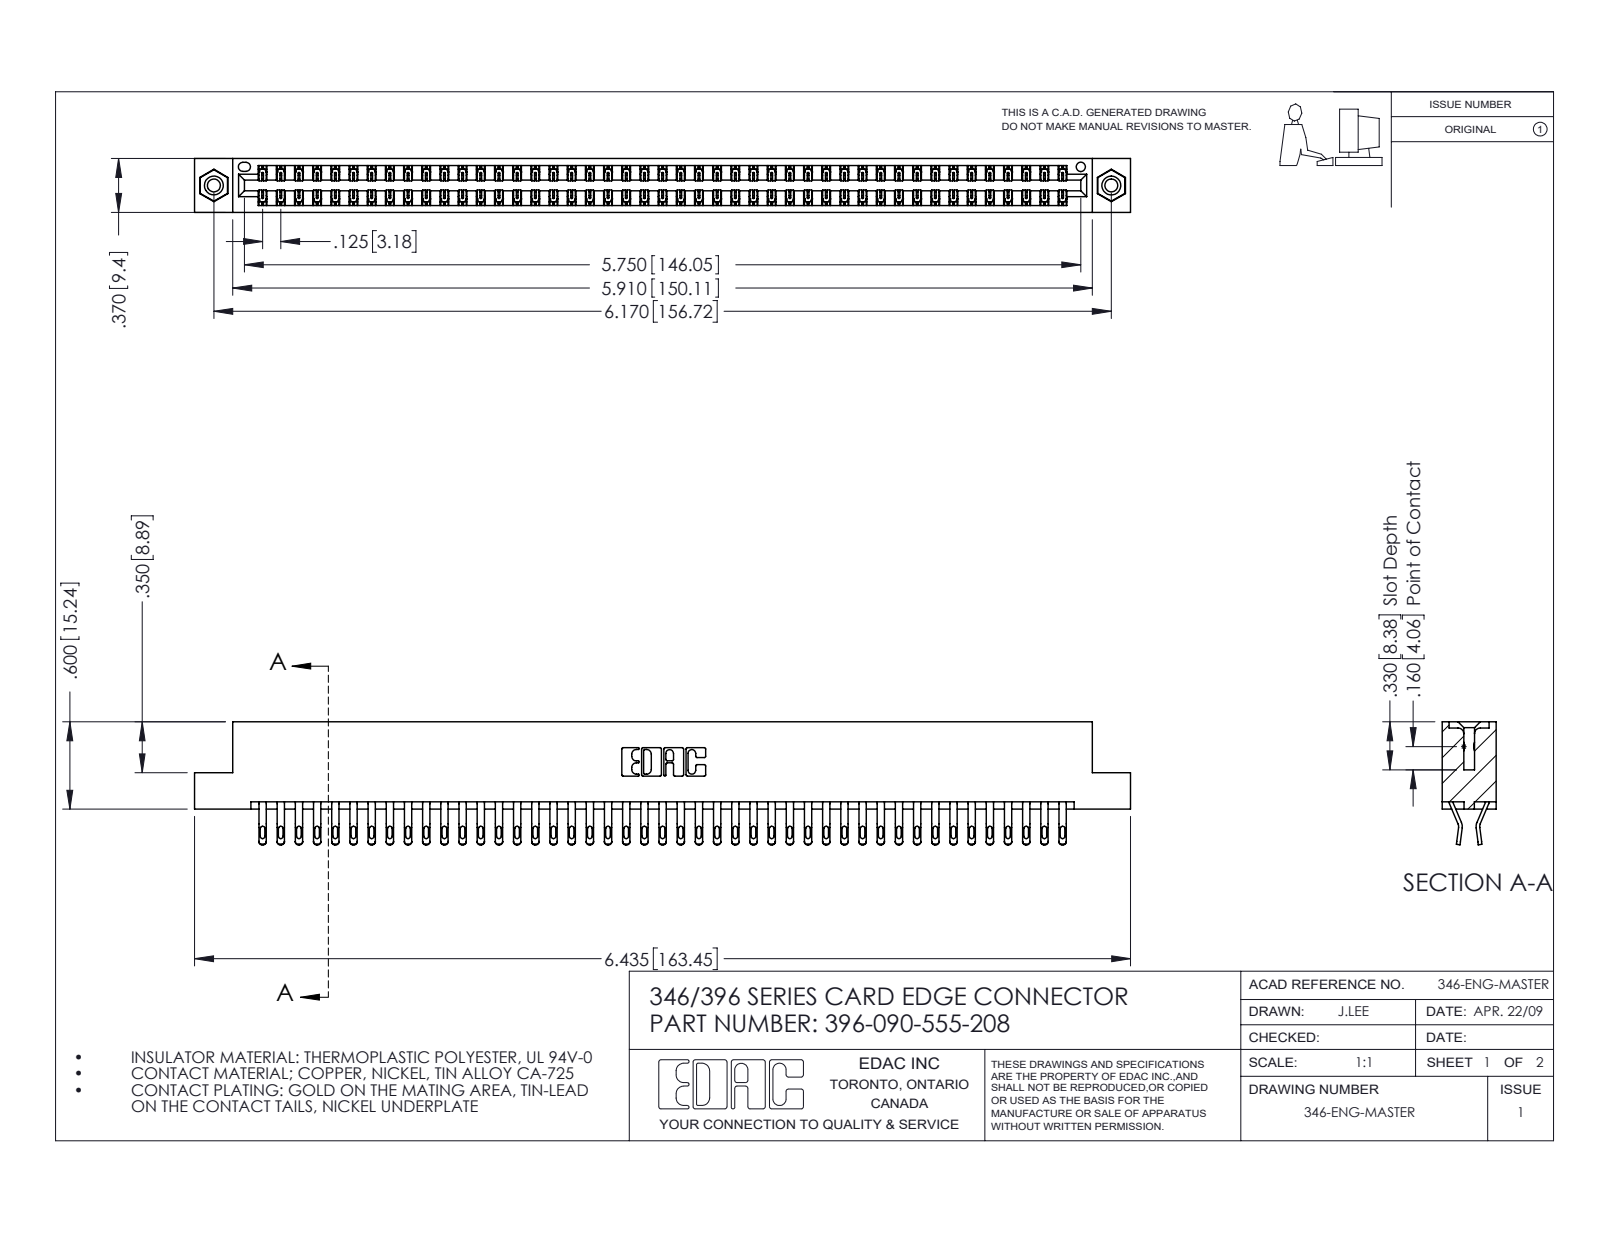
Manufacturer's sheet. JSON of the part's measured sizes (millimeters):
{"part_name": "396-090-555-208; 345-292-001_555 Tail; 345-250-001_345-250-003-102; 346 Part_Flush Mounting Lugs - 0.156 Dia-TI", "step_written_by": "SolidWorks 2016 (CONFIG_CONTROL_DESIGN)", "units": "millimeters", "bodies": {"solids": 93, "faces": 5402, "planar": 3078, "cylindrical": 2308, "other": 16}, "overall_size": [163.4, 21.5, 9.4], "volume_mm3": 16200, "surface_area_mm2": 23290, "round_holes": [[2.3, 2], [3.2, 2], [4, 2], [1.6, 1]], "round_bosses_or_shafts": [[3.9, 2]], "partial_cylinders_radius": [[0.4, 180], [0.5, 180], [0.2, 135], [0.3, 22], [0.2, 6], [0.8, 6], [0.7, 3], [0.3, 2]], "face_to_face_distances": [1.2, 8.2, 9.4, 6.4, 0.6, 1.8, 7.6, 7, 3.8, 5.6], "hole_center_spacings": [6.2, 151.4, 156.7]}
